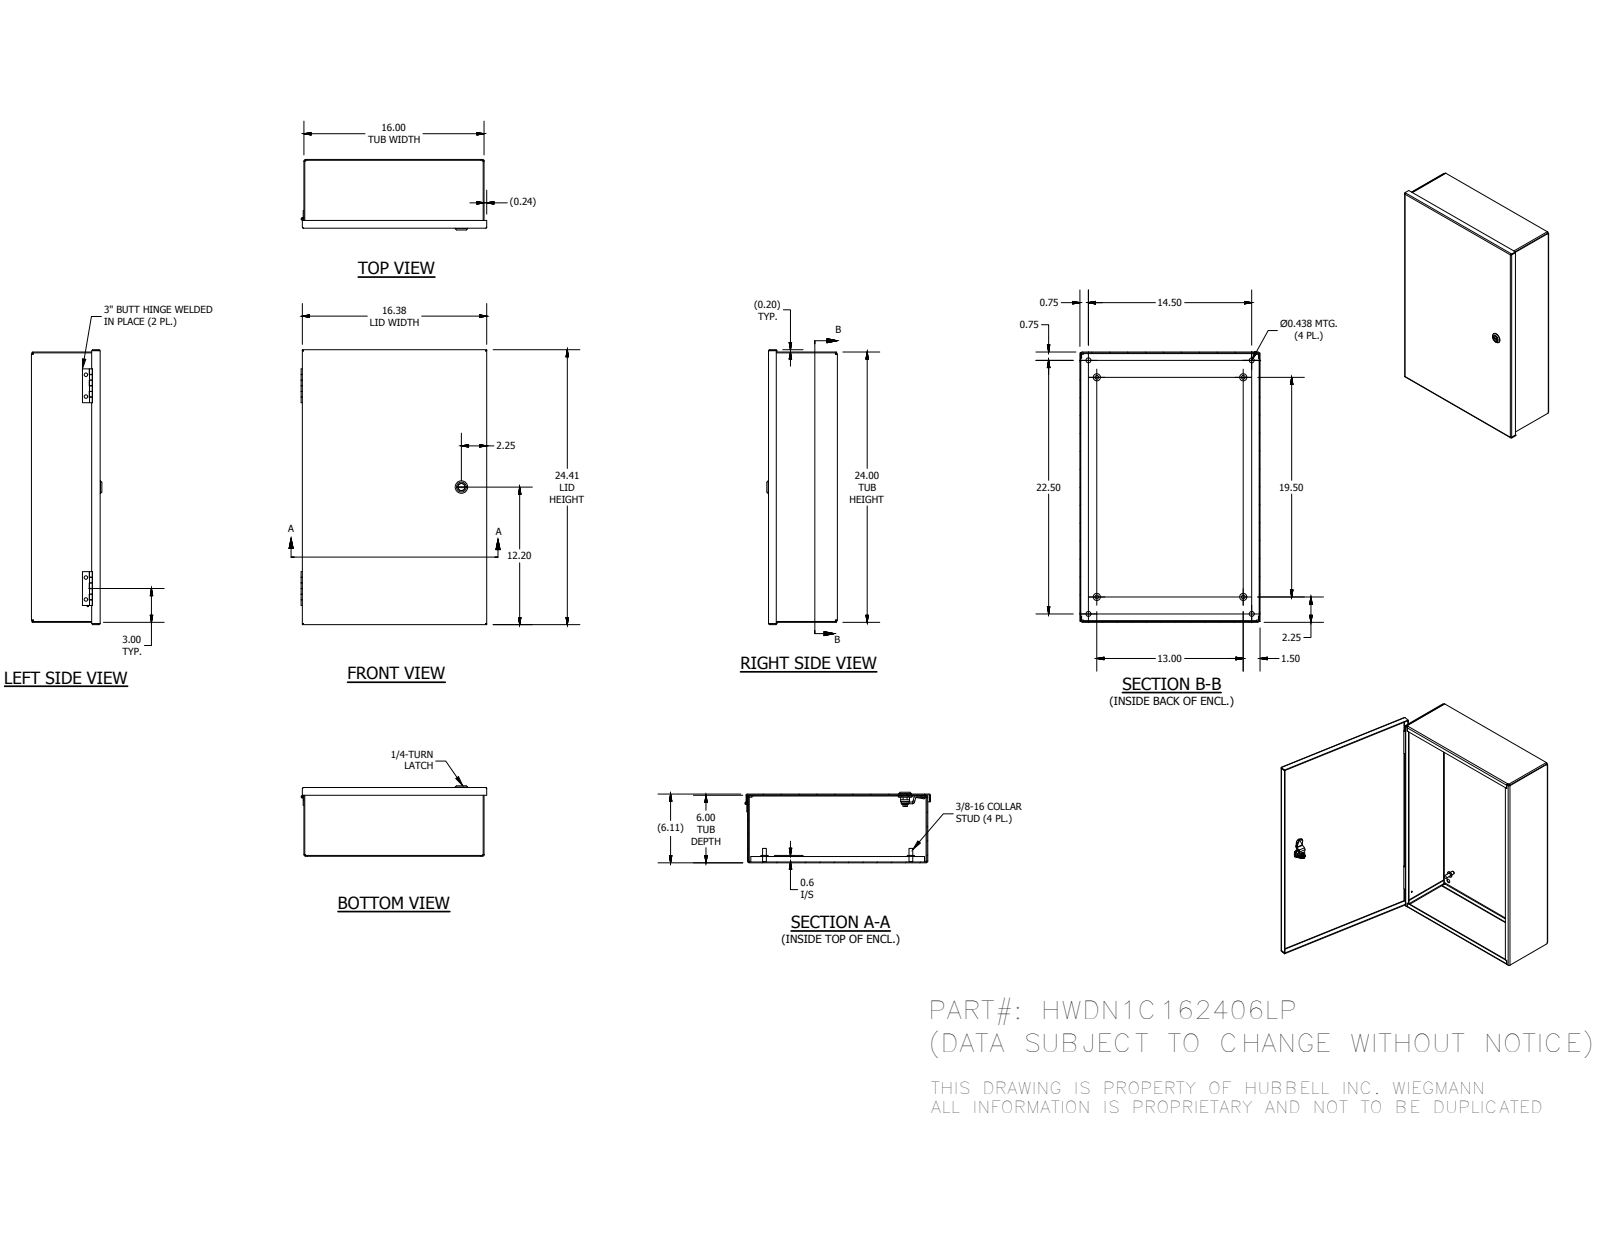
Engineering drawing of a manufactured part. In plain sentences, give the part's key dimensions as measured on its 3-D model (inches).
The part is named "N1C162406LPBLR; N1C1606LPTB; N1C1624LPLID; 1000-101-GPF_GPD (+8 more)". Its 3-D file was written by "Autodesk Inventor 2016 (AUTOMOTIVE_DESIGN)". It is 21 solids with 717 faces: 437 planar, 212 cylindrical and 68 other. Overall it measures 24.406 by 16.489 by 7.013 inches. Its volume is 106.8 cubic inches and its surface area 2 905 square inches. Round holes: 4 of diameter 0.313, 4 of diameter 0.437, 1 of diameter 0.12, 1 of diameter 0.13, 1 of diameter 0.197, 1 of diameter 0.315, 1 of diameter 0.394, 1 of diameter 0.402, 1 of diameter 0.634, 1 of diameter 0.802. Round bosses or shafts: 4 of diameter 0.625, 4 of diameter 0.33, 1 of diameter 1.102, 1 of diameter 1.063, 1 of diameter 0.906, 1 of diameter 0.78, 1 of diameter 0.622, 1 of diameter 0.598. Partial cylindrical surfaces (rounded edges, fillets, slot ends): 30 of radius 0.012, 12 of radius 0.063, 12 of radius 0.137, 10 of radius 0.02, 4 of radius 0.031, 4 of radius 0.105, 4 of radius 0.157, 3 of radius 0.016. The main face-to-face distances are 0.074, 6.781, 6.707, 6.855, 15.926, 23.926, 15.852, 16, 23.852, 24. The hole center spacings are 1.94, 11.32, 14.5, 17.373, 18, 22.5, 26.767, 0.611.
